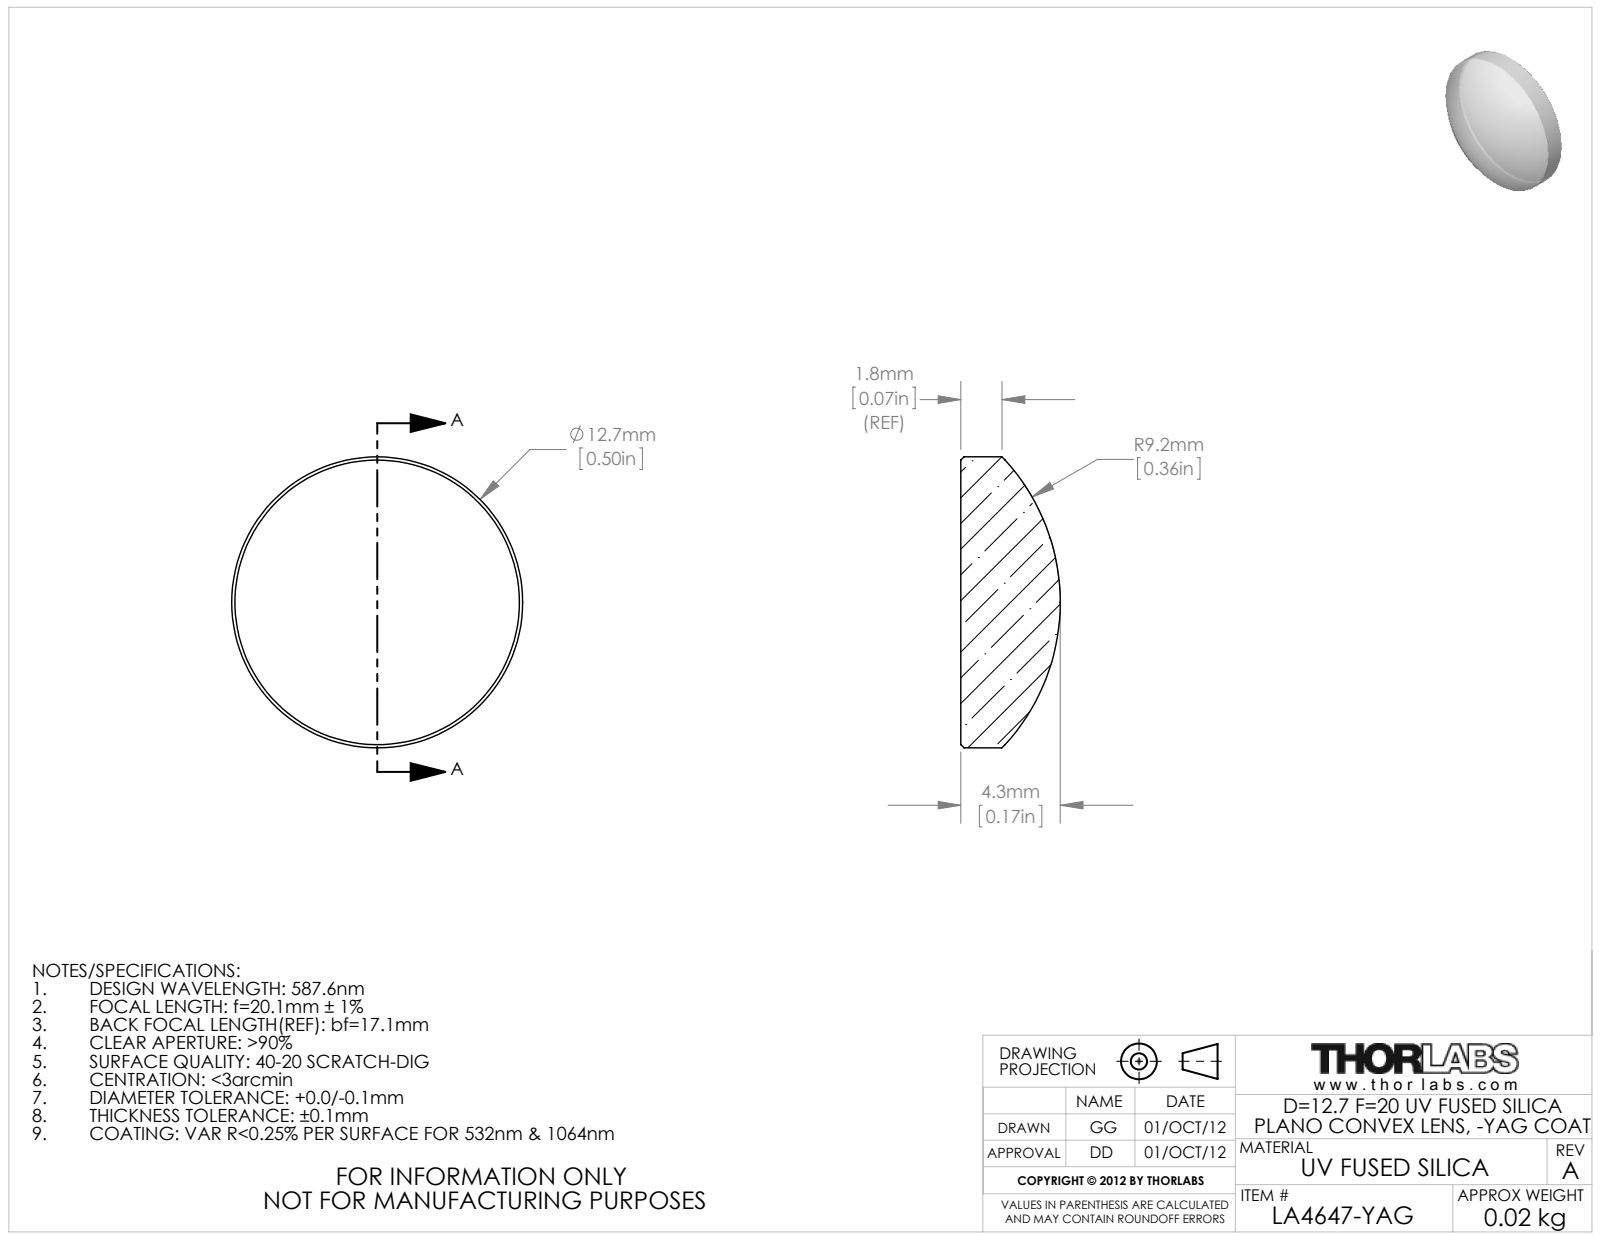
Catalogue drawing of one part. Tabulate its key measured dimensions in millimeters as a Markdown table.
| quantity | value |
| --- | --- |
| part name | 24948-E0W |
| STEP written by | SolidWorks 2011 (CONFIG_CONTROL_DESIGN) |
| units | millimeters |
| bodies | 1 solid, 9 faces (1 planar, 2 cylindrical, 6 other) |
| overall size | 12.7 × 12.7 × 4.34 |
| volume | 397 mm³ |
| surface area | 342 mm² |
| round bosses / shafts (diameter × count) | 12.7 × 1 |
